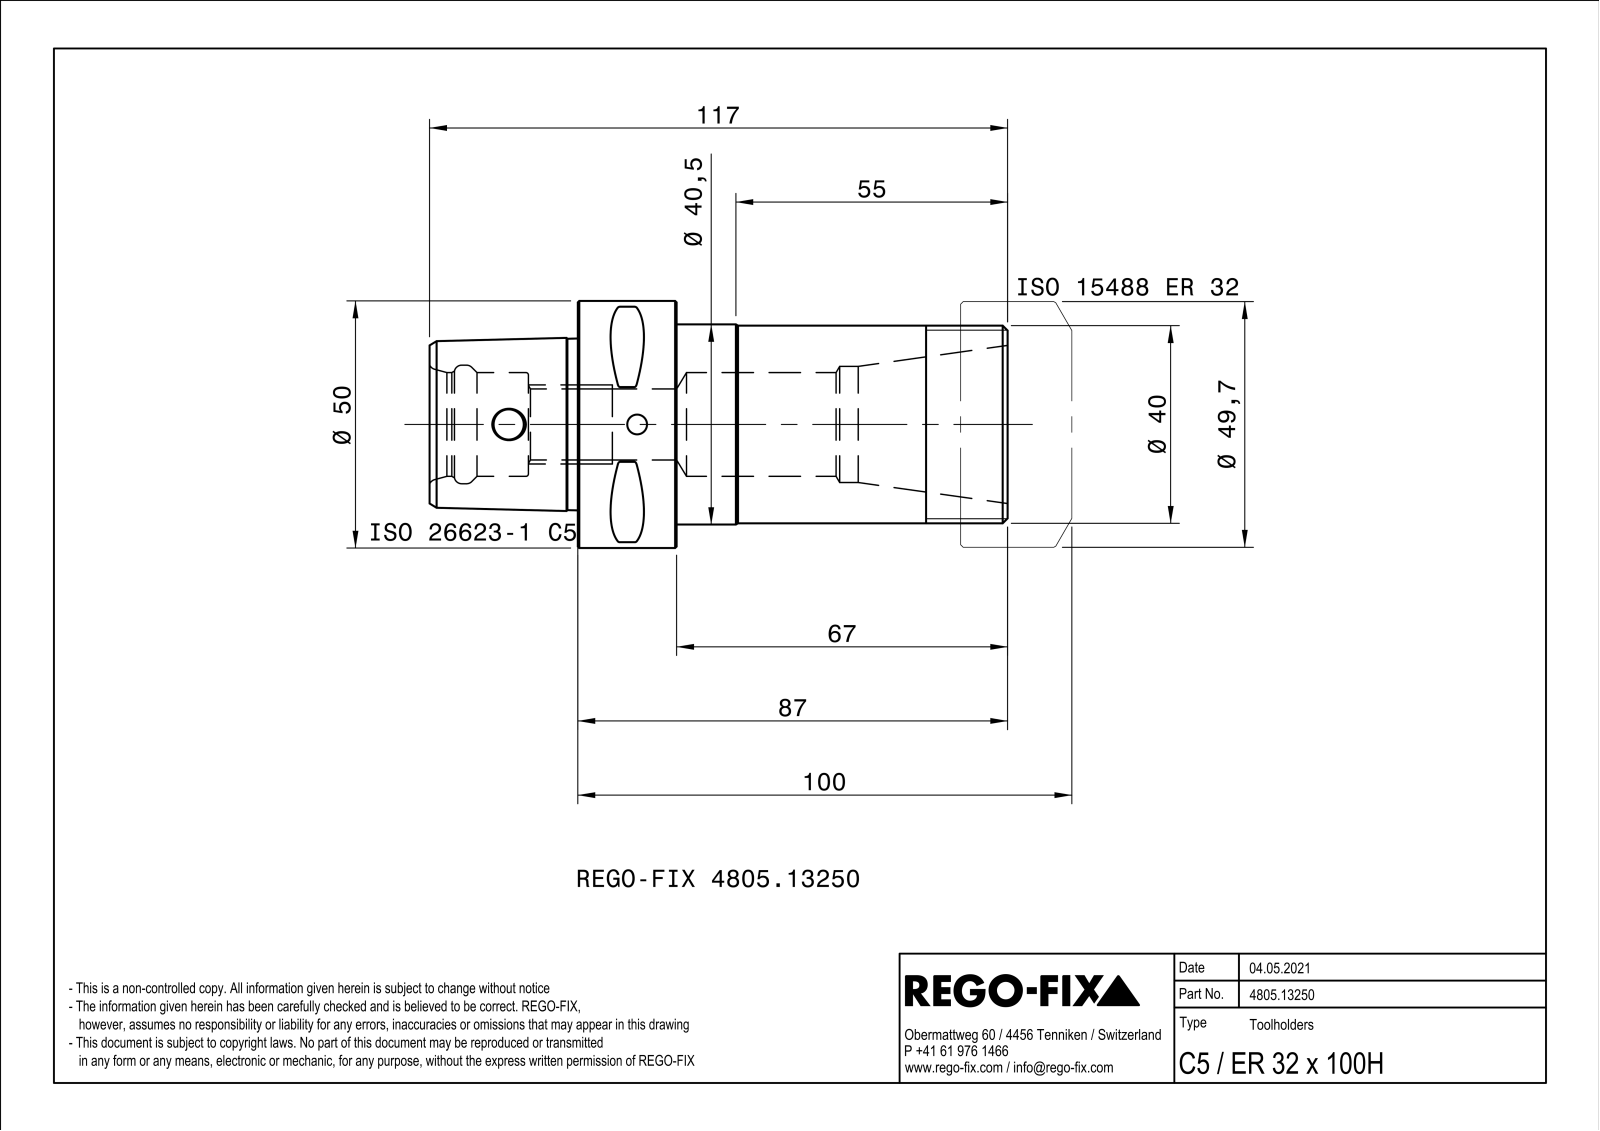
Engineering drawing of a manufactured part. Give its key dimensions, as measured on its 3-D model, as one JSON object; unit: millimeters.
{"part_name": "NOCUT", "step_written_by": "SIEMENS PLM Software Solid Edge ST10 (AUTOMOTIVE_DESIGN)", "units": "millimeters", "bodies": {"solids": 1, "faces": 108, "planar": 20, "cylindrical": 25, "other": 63}, "overall_size": [117, 50, 50], "volume_mm3": 105901, "surface_area_mm2": 25901, "round_holes": [[4, 1], [6.1, 1], [14.38, 1], [21, 1], [23.5, 1], [24, 1]], "round_bosses_or_shafts": [[50, 1], [40.5, 1], [40, 1]], "partial_cylinders_radius": [[0.5, 8], [4, 1]], "face_to_face_distances": [20, 30, 50, 67, 87, 117, 19.18, 44.4, 97, 10], "hole_center_spacings": [26]}
